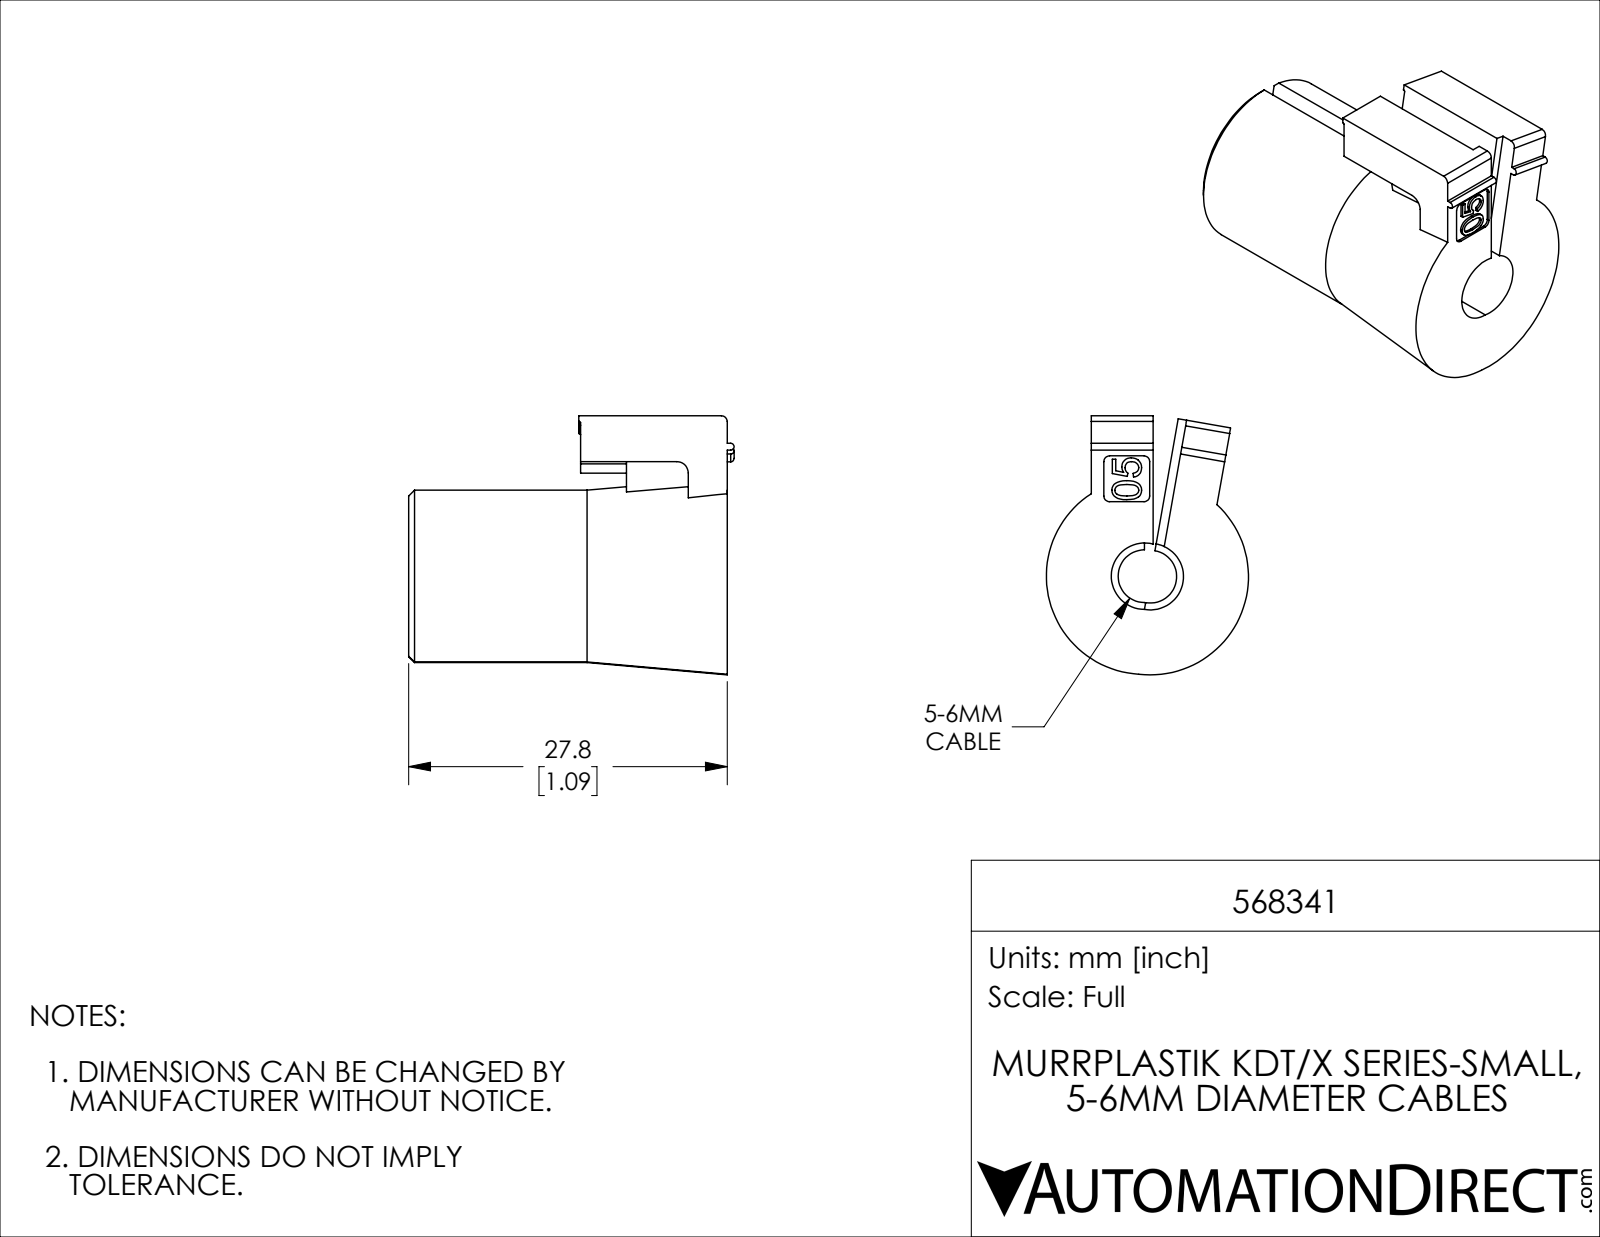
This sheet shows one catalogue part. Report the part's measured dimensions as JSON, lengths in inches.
{"part_name": "568341", "step_written_by": "SolidWorks 2019 (CONFIG_CONTROL_DESIGN)", "units": "inches", "bodies": {"solids": 1, "faces": 115, "planar": 59, "cylindrical": 24, "other": 32}, "overall_size": [1.118, 0.89, 0.695], "volume_in3": 0.308, "surface_area_in2": 4.642, "partial_cylinders_radius": [[0.02, 6], [0.004, 2], [0.012, 2], [0.039, 2], [0.091, 2], [0.114, 2], [0.295, 2]], "face_to_face_distances": [1.094, 0.183, 0.157, 0.03, 0.504, 0.591, 0.213, 0.154, 0.059, 0.445]}
